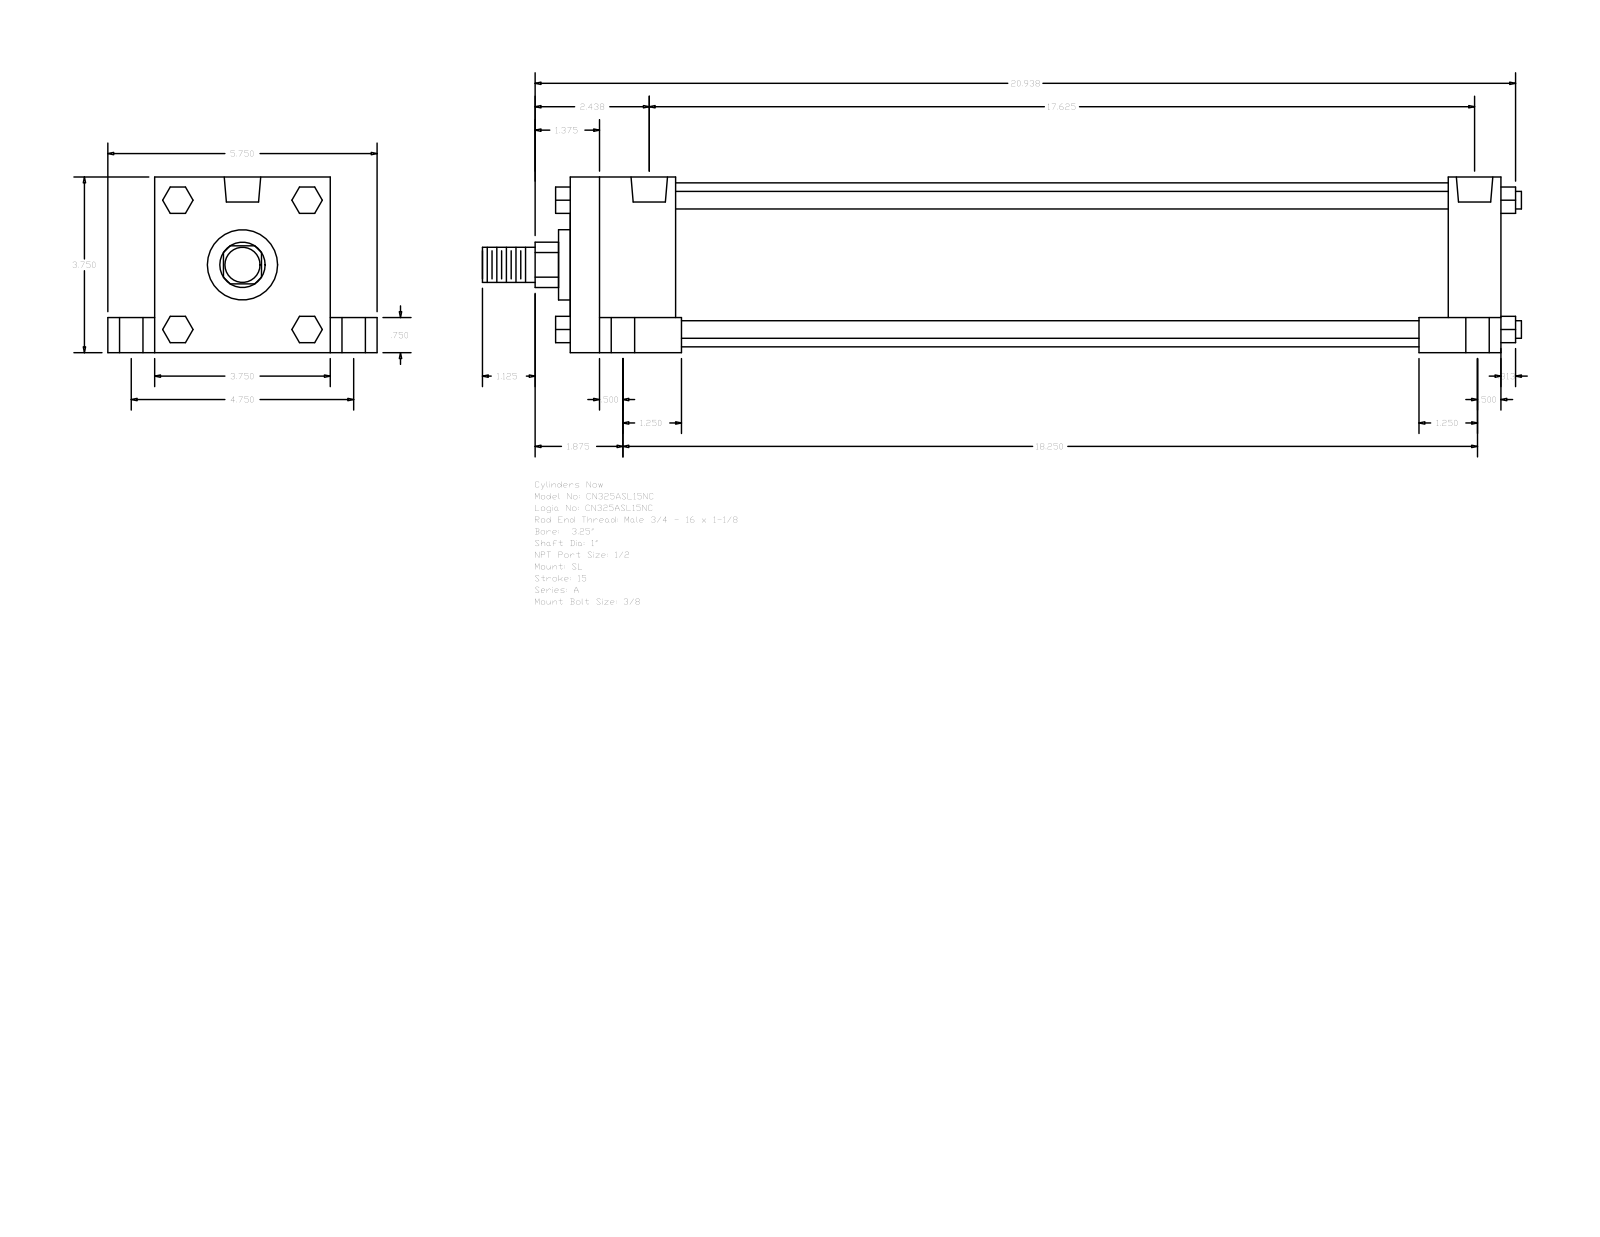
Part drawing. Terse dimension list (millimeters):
name: A_SL__0325_1
written by: GSSL Pune (CONFIG_CONTROL_DESIGN)
unit: mm
bodies: 0 solids, 150 faces (114 planar, 36 cylindrical, 0 other)
size: 563.56 × 146.05 × 95.25
holes: 4× ⌀8.73, 4× ⌀12.7, 4× ⌀19.05, 2× ⌀19.77
bosses: 4× ⌀9.53, 1× ⌀88.9, 1× ⌀38.1, 1× ⌀25.4, 1× ⌀19.05
rounds: 1× R12.29
face distances: 95.24, 504.83, 19.05, 25.41, 120.65, 76.19, 57.15, 476.25, 419.1, 447.68
hole spacings: 3.18, 60.35, 60.52, 62, 62.81, 120.66, 441.32, 444.5
